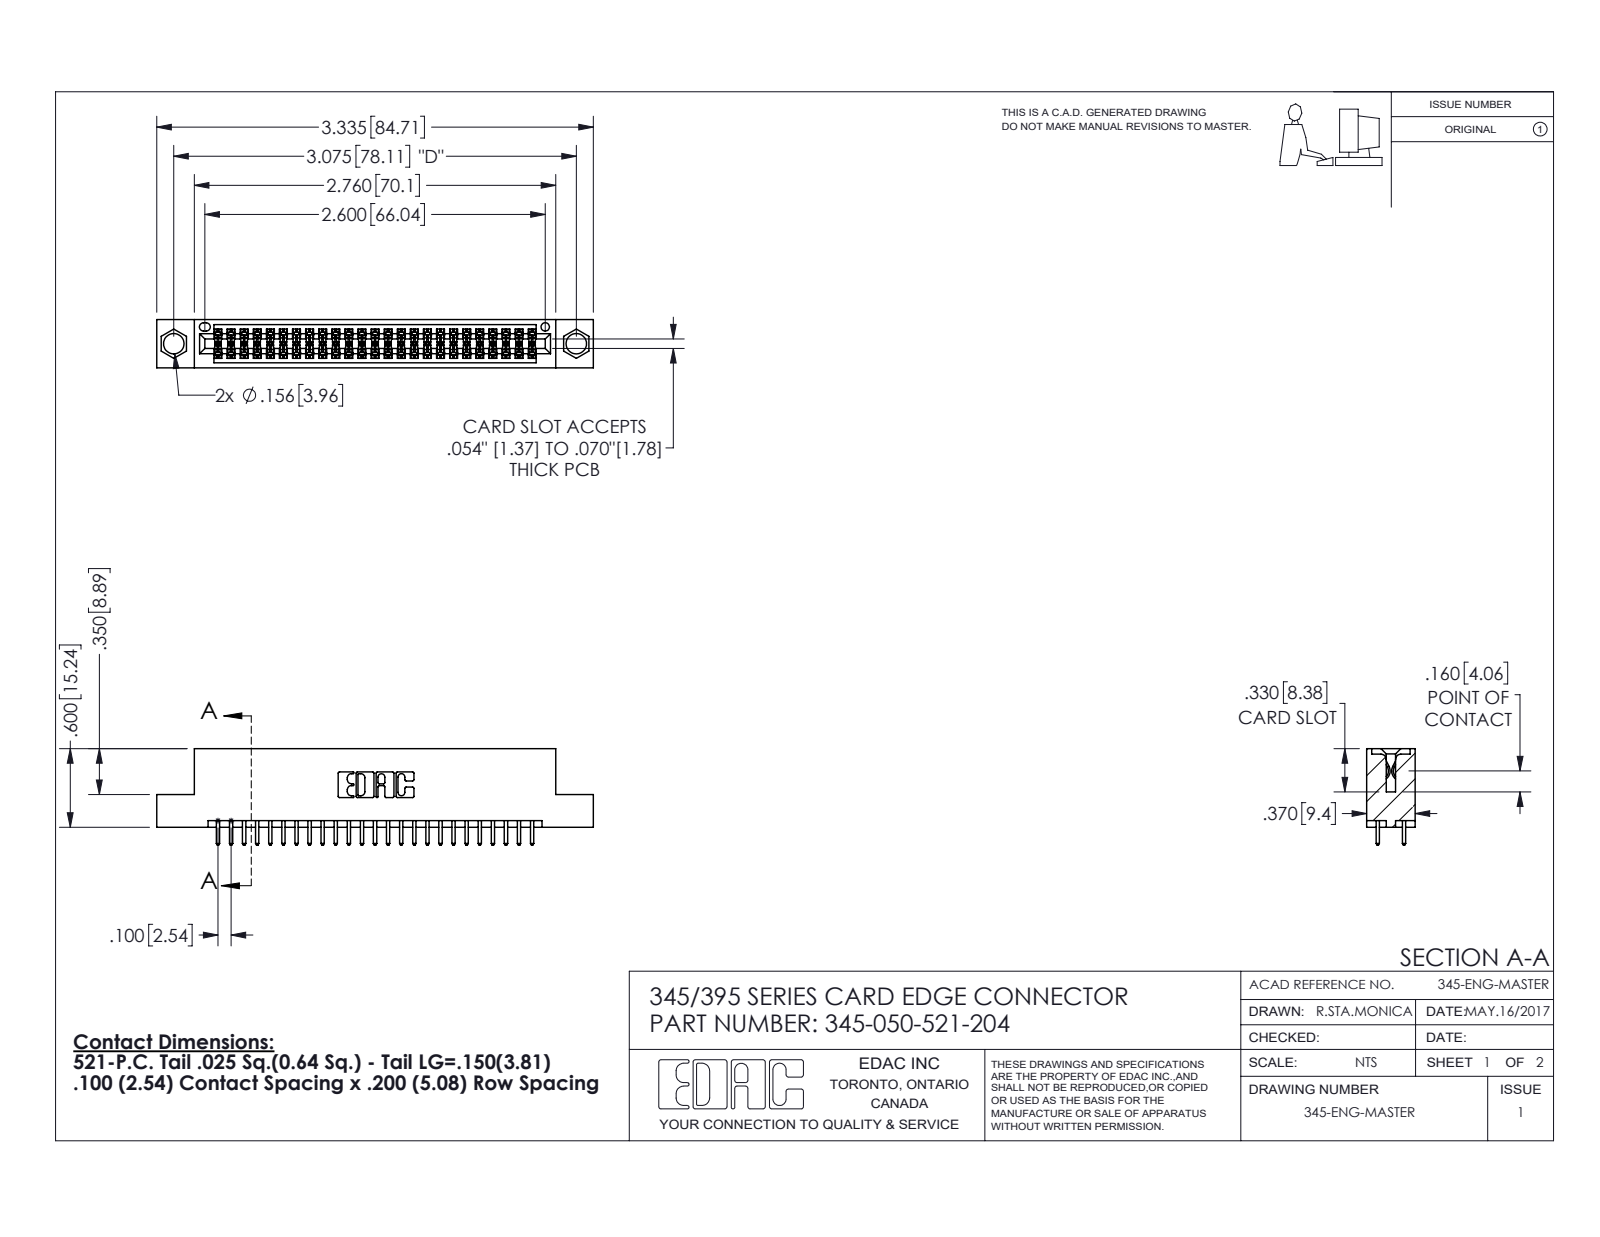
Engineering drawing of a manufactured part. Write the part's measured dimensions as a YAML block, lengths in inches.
part_name: "345-050-521-204; 345 Part_Flush Mounting Lugs - 0.156 Dia-TI; 345-292-001_345-293-121"
step_written_by: "SolidWorks 2020 (CONFIG_CONTROL_DESIGN)"
units: inches
bodies: {solids: 51, faces: 2640, planar: 1744, cylindrical: 896, other: 0}
overall_size: [3.335, 0.737, 0.37]
volume: 0.485
surface_area: 17.26
round_holes:
  - {diameter: 0.156, count: 2}
  - {diameter: 0.064, count: 1}
partial_cylinders:
  - {radius: 0.006, count: 75}
  - {radius: 0.01, count: 50}
  - {radius: 0.01, count: 22}
  - {radius: 0.007, count: 6}
  - {radius: 0.031, count: 6}
  - {radius: 0.026, count: 3}
  - {radius: 0.014, count: 2}
  - {radius: 0.019, count: 2}
face_to_face_distances: [0.298, 0.072, 0.2, 0.37, 0.098, 0.272, 0.025, 0.225, 0.175, 0.149]
hole_center_spacings: [0.27, 2.84, 3.075]
